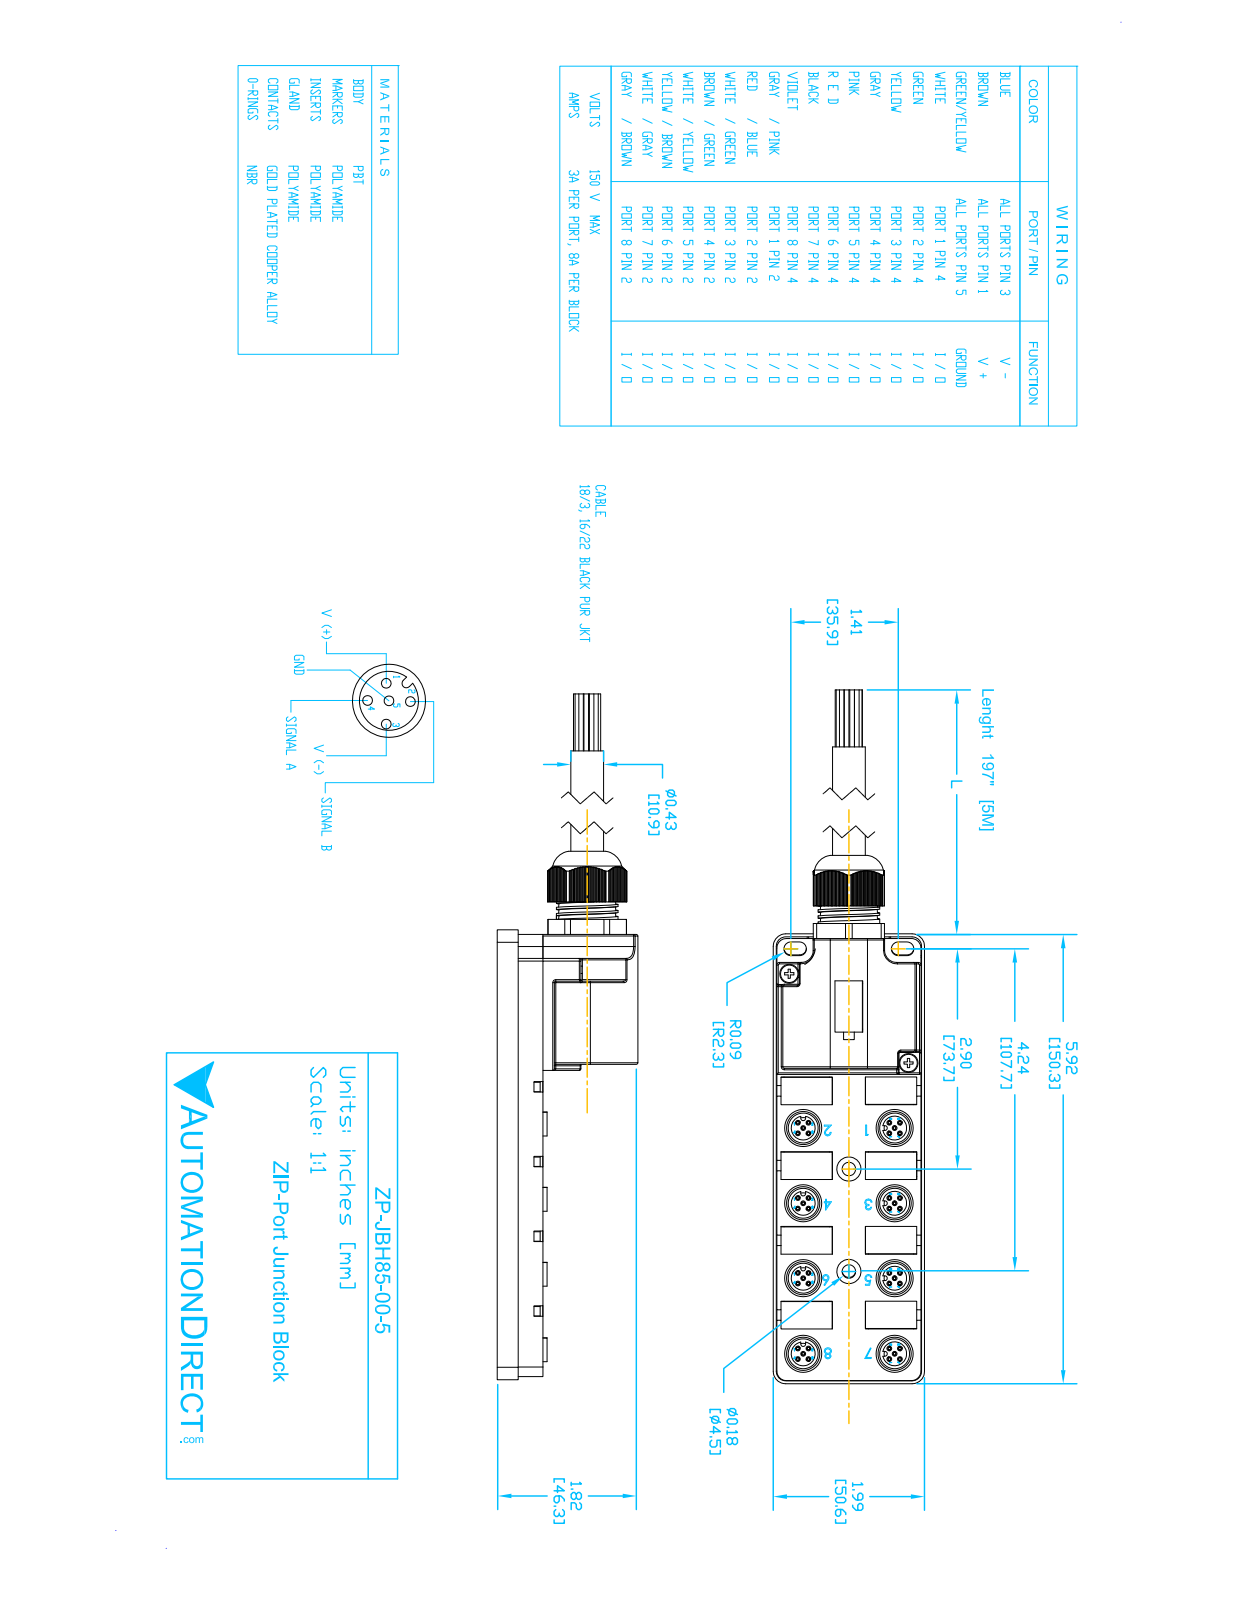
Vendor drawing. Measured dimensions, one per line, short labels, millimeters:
name: ZP-JBH85-00-5
written by: SolidWorks 2017 (AUTOMOTIVE_DESIGN)
unit: mm
bodies: 10 solids, 1533 faces (863 planar, 395 cylindrical, 275 other)
size: 232.9 × 50.6 × 47
volume: 173 200 mm³; area: 40 540 mm²
holes: 40× ⌀1.1, 40× ⌀1.6, 8× ⌀11.1, 8× ⌀12.4, 2× ⌀4.5, 2× ⌀6.4, 2× ⌀6.6, 2× ⌀8.1, 1× ⌀7.6, 1× ⌀9.4, 1× ⌀12.4, 1× ⌀15.2
bosses: 7× ⌀8, 2× ⌀5.8, 1× ⌀20.6, 1× ⌀8.8, 1× ⌀8
rounds: 34× R0.5, 8× R0.8, 4× R0.9, 4× R2.3, 4× R4.2, 2× R3.2, 2× R4, 2× R15.9
face distances: 15.2, 0.9, 0.9, 0.8, 15.2, 14.4, 48.2, 15.1, 49.4, 1.2
hole spacings: 2.5, 3.5, 30.6, 28.9, 32.4, 25.2, 39.6, 5
